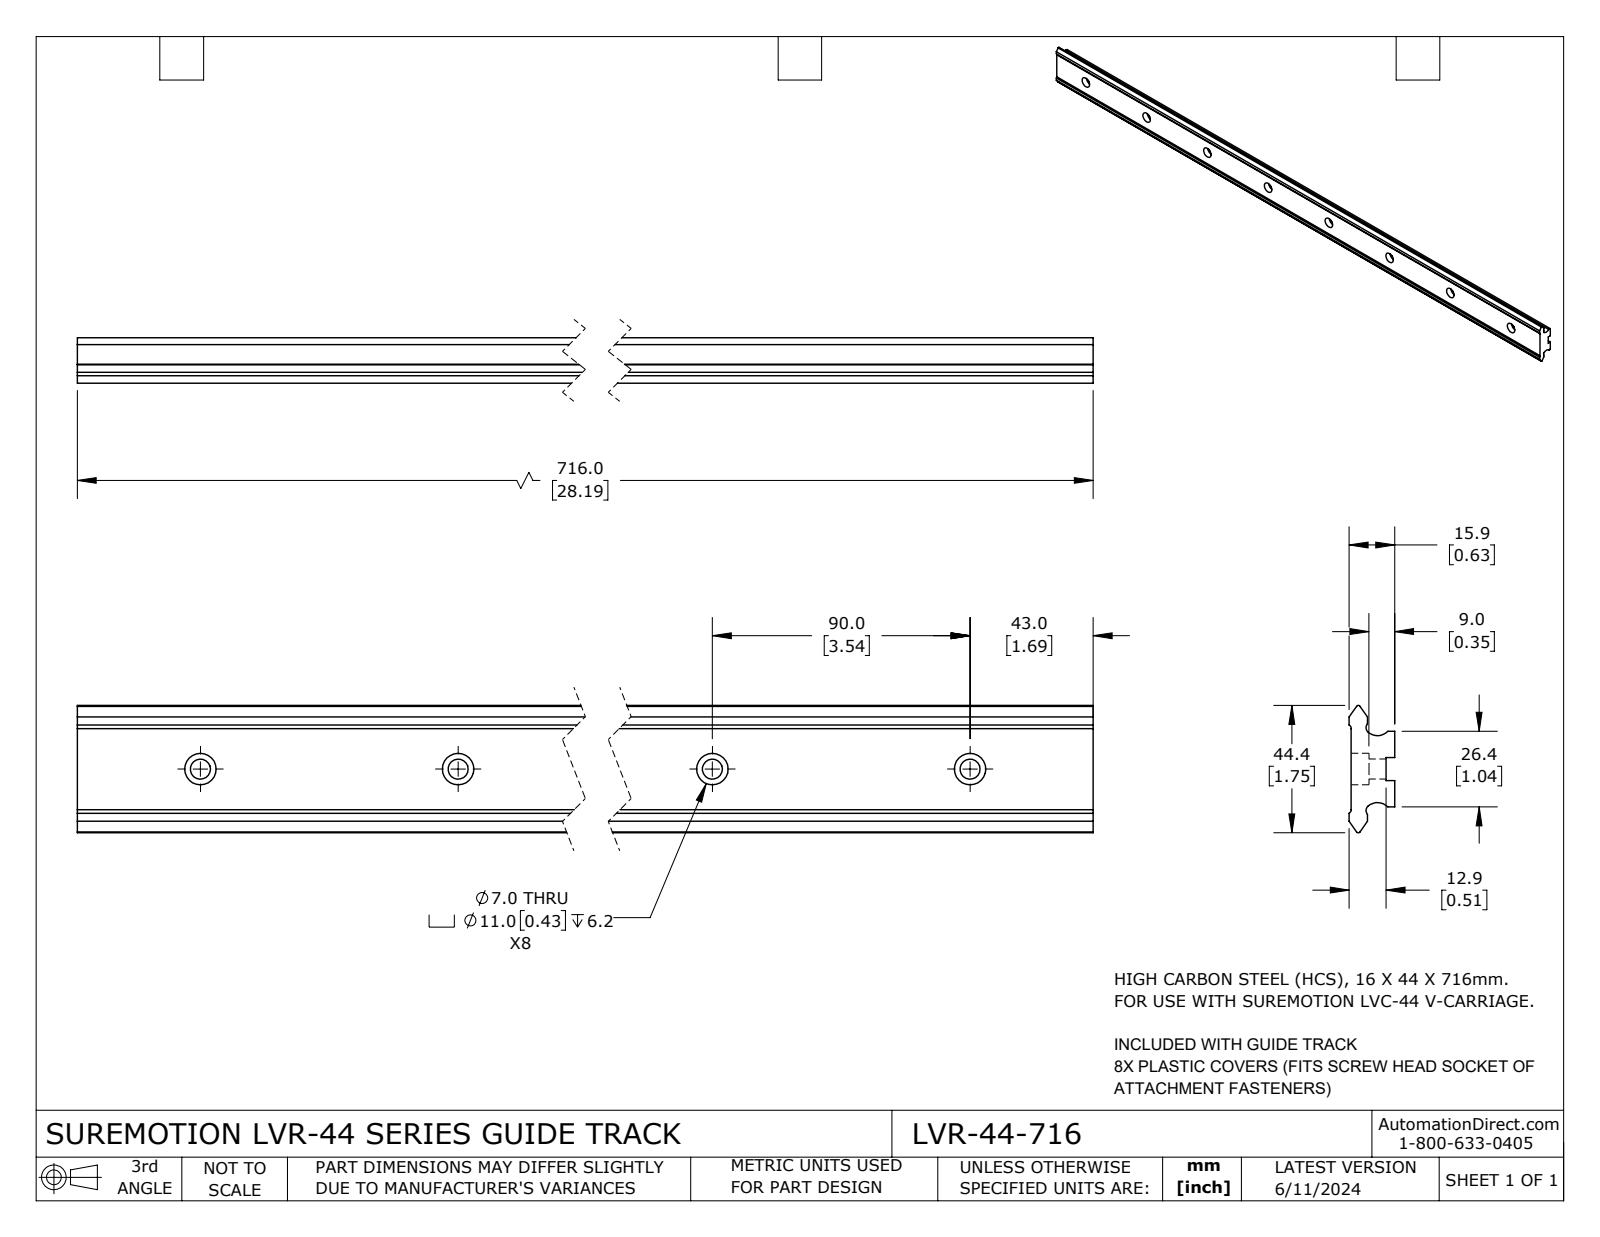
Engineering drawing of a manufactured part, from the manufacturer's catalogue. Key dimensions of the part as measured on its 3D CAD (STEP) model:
Part name (STEP PRODUCT): LVR-44-716
STEP written by: SolidWorks 2023 (CONFIG_CONTROL_DESIGN)
Units: millimetres
Bodies: 1 solid, 68 faces (26 planar, 42 cylindrical, 0 other)
Overall size (bounding box): 716 × 44.45 × 15.91
Volume: 316 253 mm³ · Surface area: 90 067 mm²
Round holes (diameter × count): ⌀7 ×8, ⌀11 ×8
Partial cylindrical surfaces — rounded edges, fillets, slot ends (radius × count): R0.76 ×2, R1.5 ×2, R2.13 ×2, R4.98 ×2
Main face-to-face distances: 15.2, 26.16, 3, 12.2, 15.91, 12.91, 0.71, 9.2, 17.2, 9.48
Hole centre spacings: 90, 180, 270, 360, 450, 540, 630
